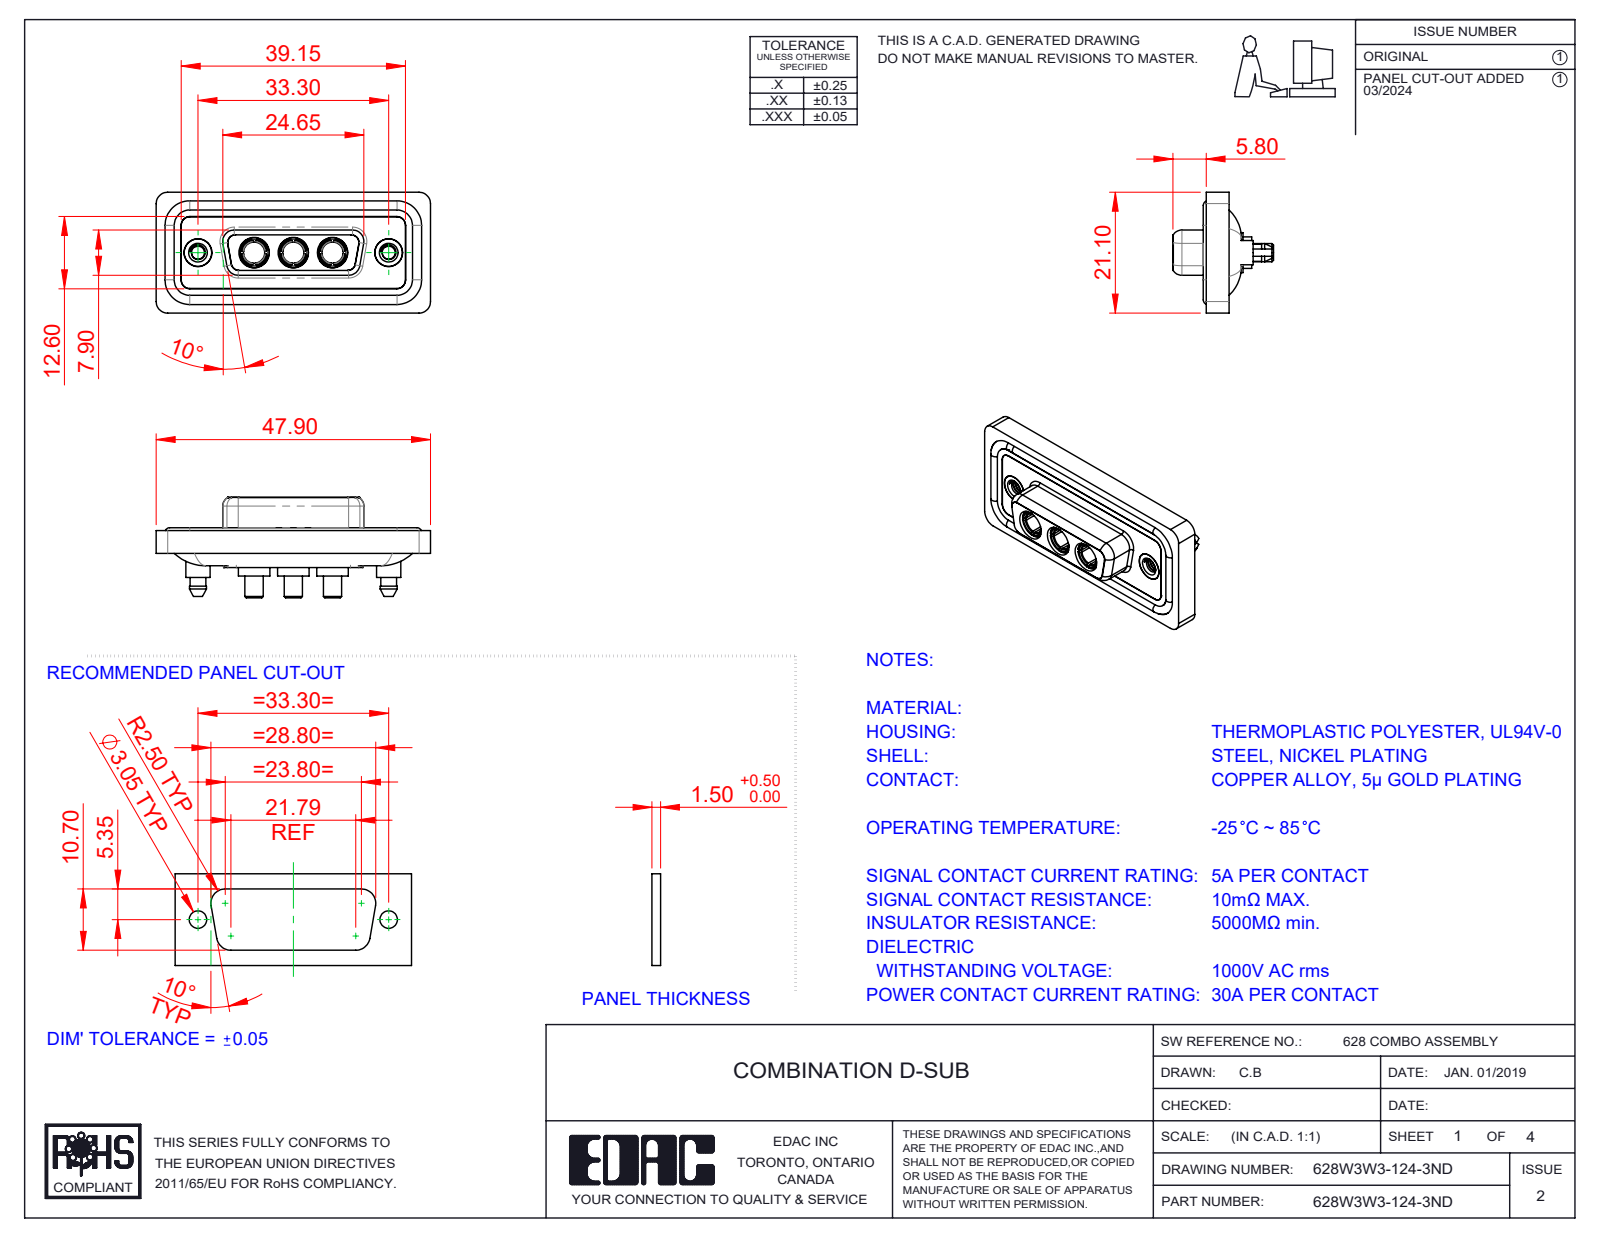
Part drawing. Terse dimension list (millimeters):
name: 628Combo Shell Front_15 Contacts; 628Combo Waterproof Housing_15 Contacts; 628Combo Threaded Boardlock_D; 628W3W3-124-3ND (+3 more)
written by: SolidWorks 2023 (CONFIG_CONTROL_DESIGN)
unit: mm
bodies: 13 solids, 674 faces (208 planar, 305 cylindrical, 161 other)
size: 47.9 × 21.1 × 17.55
volume: 6 183 mm³; area: 10 092 mm²
holes: 5× ⌀4.85, 3× ⌀3.7, 3× ⌀5.3, 2× ⌀2.26, 2× ⌀4, 2× ⌀4.05, 2× ⌀5
bosses: 4× ⌀1.6, 3× ⌀5.5, 3× ⌀5.2, 3× ⌀4.96, 3× ⌀4.75, 3× ⌀3.75, 3× ⌀3.2, 2× ⌀5.4
rounds: 24× R1.5, 20× R2, 12× R1.35, 10× R1.6, 4× R0.25, 4× R0.5, 4× R0.6, 4× R0.65
face distances: 0.4, 1.8, 1.6, 0.5, 7.45, 1.1, 2.9, 5.65, 7.05, 6.6
hole spacings: 6.85, 9.8, 16.65, 23.5, 13.7, 33.3
